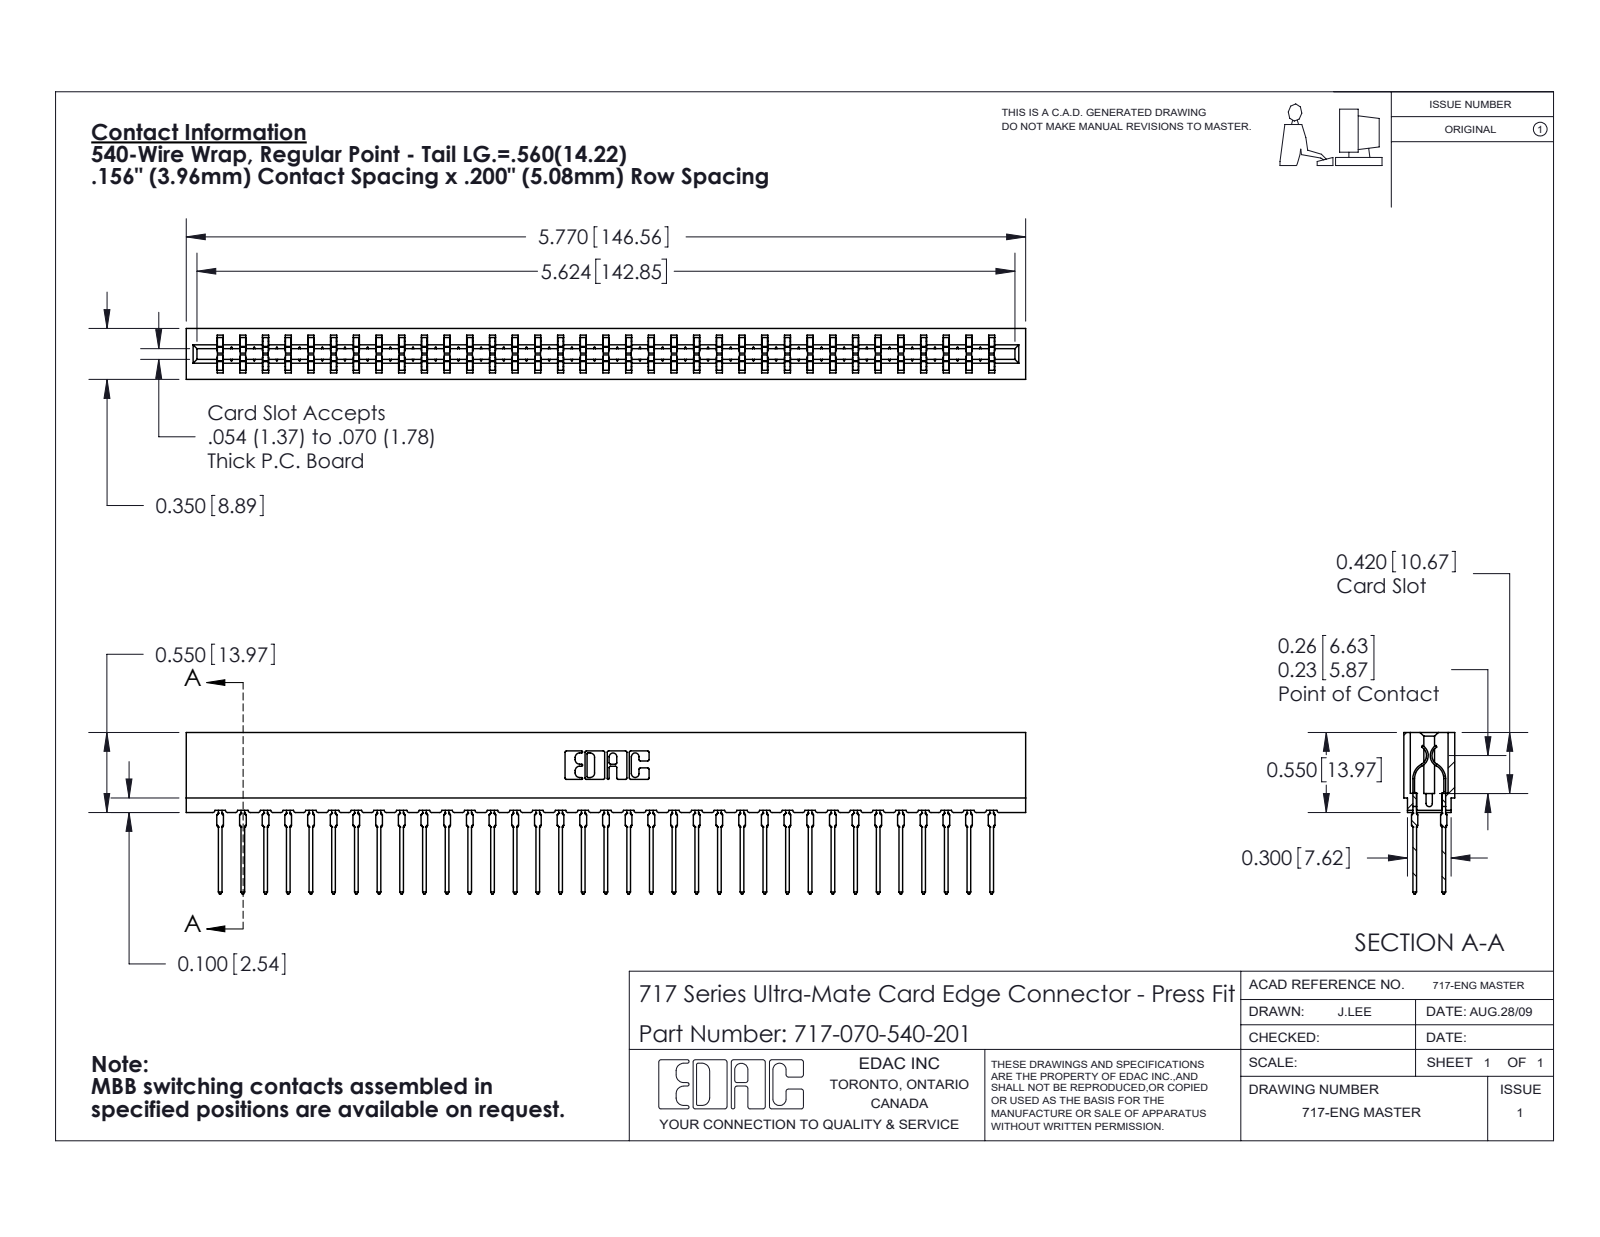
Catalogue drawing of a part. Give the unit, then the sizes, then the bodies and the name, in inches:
Units: inches
Overall size (bounding box): 5.77 × 1.109 × 0.35
Partial cylindrical surfaces — rounded edges, fillets, slot ends (radius × count): R0.021 ×140, R0.015 ×70, R0.01 ×22, R0.005 ×8, R0.011 ×8, R0.007 ×6, R0.031 ×6, R0.026 ×3
Main face-to-face distances: 0.212, 0.138, 0.35, 0.063, 0.287, 0.076, 0.149, 0.074, 0.087, 0.263
Volume: 0.789 in³ · Surface area: 31.93 in²
Bodies: 71 solids, 6394 faces (3309 planar, 1265 cylindrical, 1820 other)
Part name (STEP PRODUCT): 717-070-540-201; 717 Part_Insulator Option - 06; 745-292-001_540
STEP written by: SolidWorks 2020 (CONFIG_CONTROL_DESIGN)
